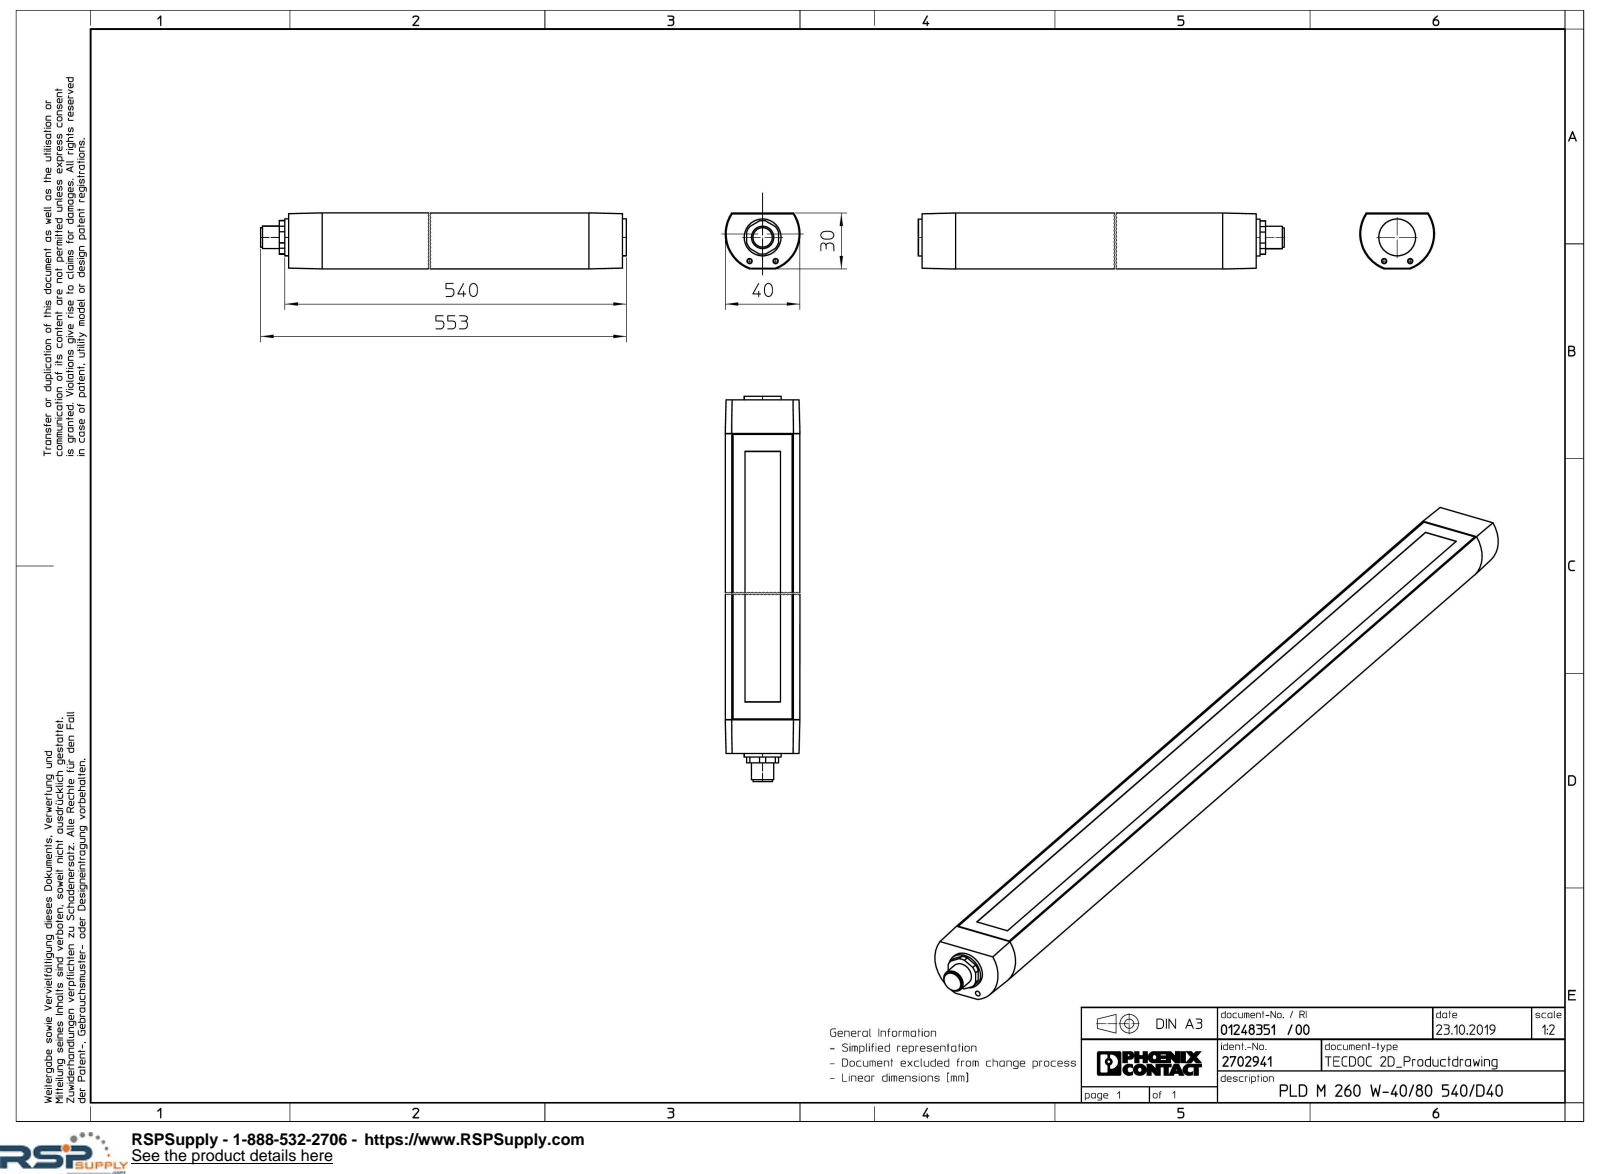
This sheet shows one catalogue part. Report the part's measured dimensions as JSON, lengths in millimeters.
{"part_name": "PLD_M_260_W_40_80_540_D40-select", "step_written_by": "Creo Elements/Direct Modeling 20.1A 29-Sep-2018 (C) Parametric Technology GmbH (AUTOMOTIVE_DESIGN)", "units": "millimeters", "bodies": {"solids": 1, "faces": 61, "planar": 33, "cylindrical": 16, "other": 12}, "overall_size": [553, 40, 29.95], "volume_mm3": 556812, "surface_area_mm2": 67314, "round_bosses_or_shafts": [[19.75, 1], [12, 1], [10.4, 1]], "partial_cylinders_radius": [[9, 1], [20, 1]], "face_to_face_distances": [29.75, 29.85, 29.95, 536, 2, 538, 41.93, 41.95, 5, 541]}
